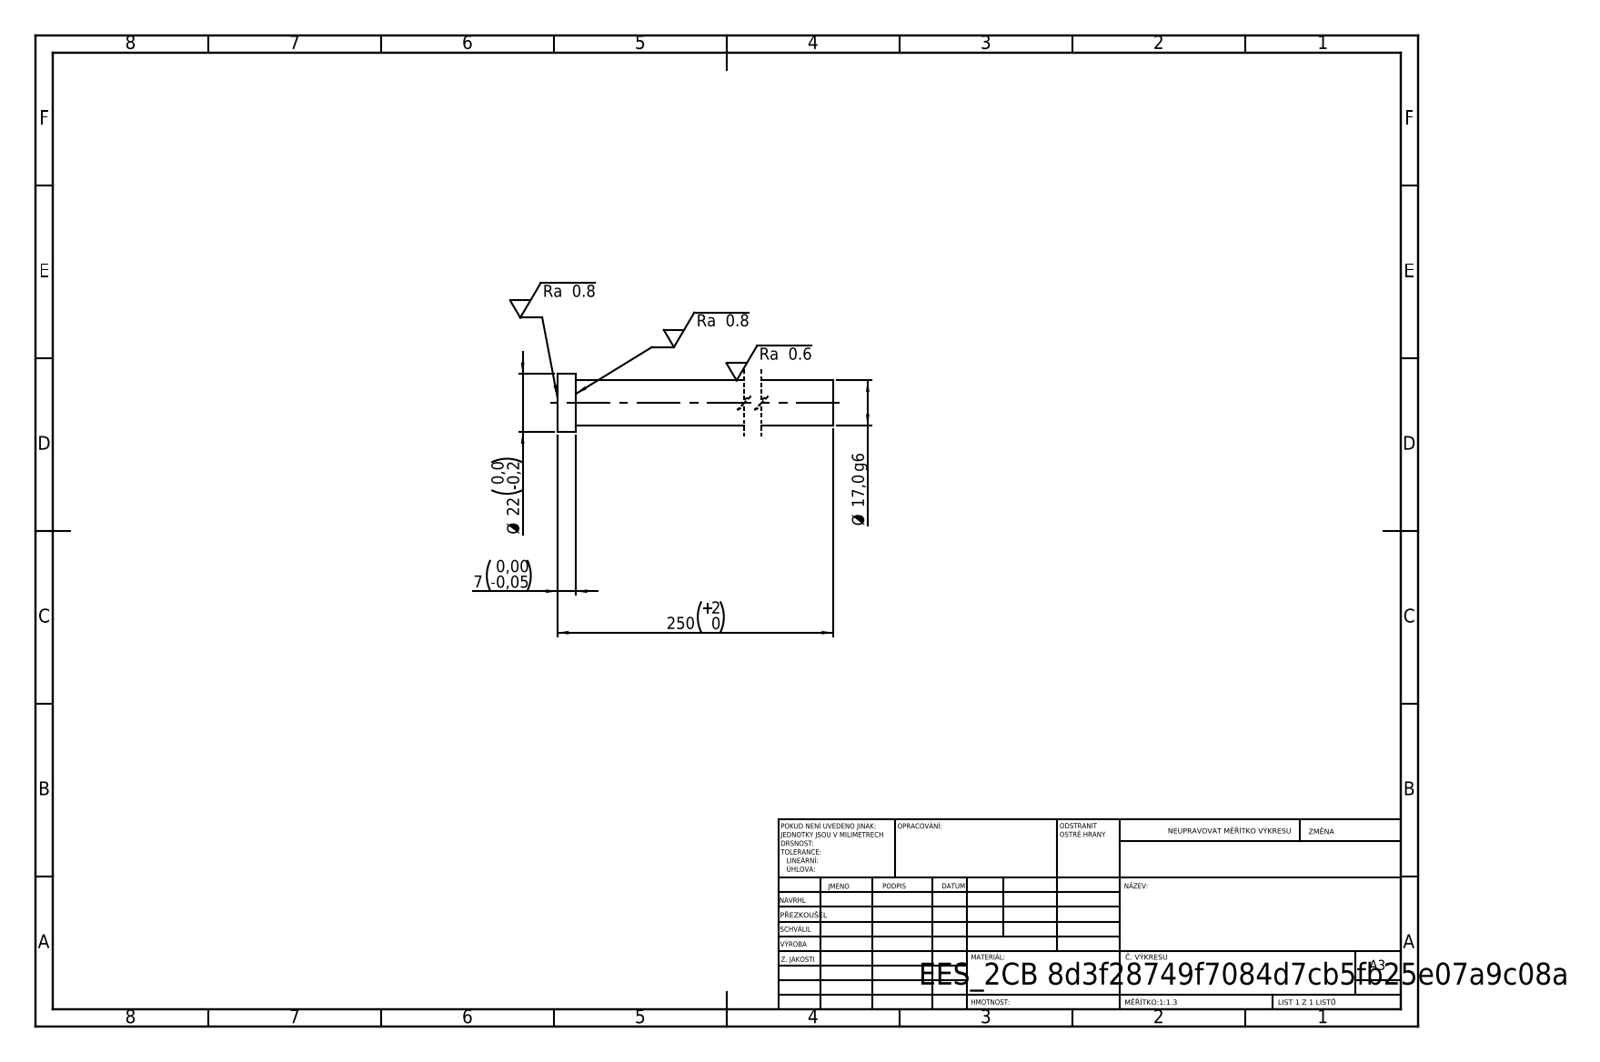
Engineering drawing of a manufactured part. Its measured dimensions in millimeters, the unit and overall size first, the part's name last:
Units: millimetres
Overall size (bounding box): 250 × 22 × 22
Round bosses / shafts (diameter × count): ⌀22 ×1, ⌀17 ×1
Main face-to-face distances: 250, 7, 243
Volume: 57 817 mm³ · Surface area: 14 222 mm²
Bodies: 1 solid, 7 faces (3 planar, 4 cylindrical, 0 other)
STEP written by: SolidWorks 2019 (CONFIG_CONTROL_DESIGN)
